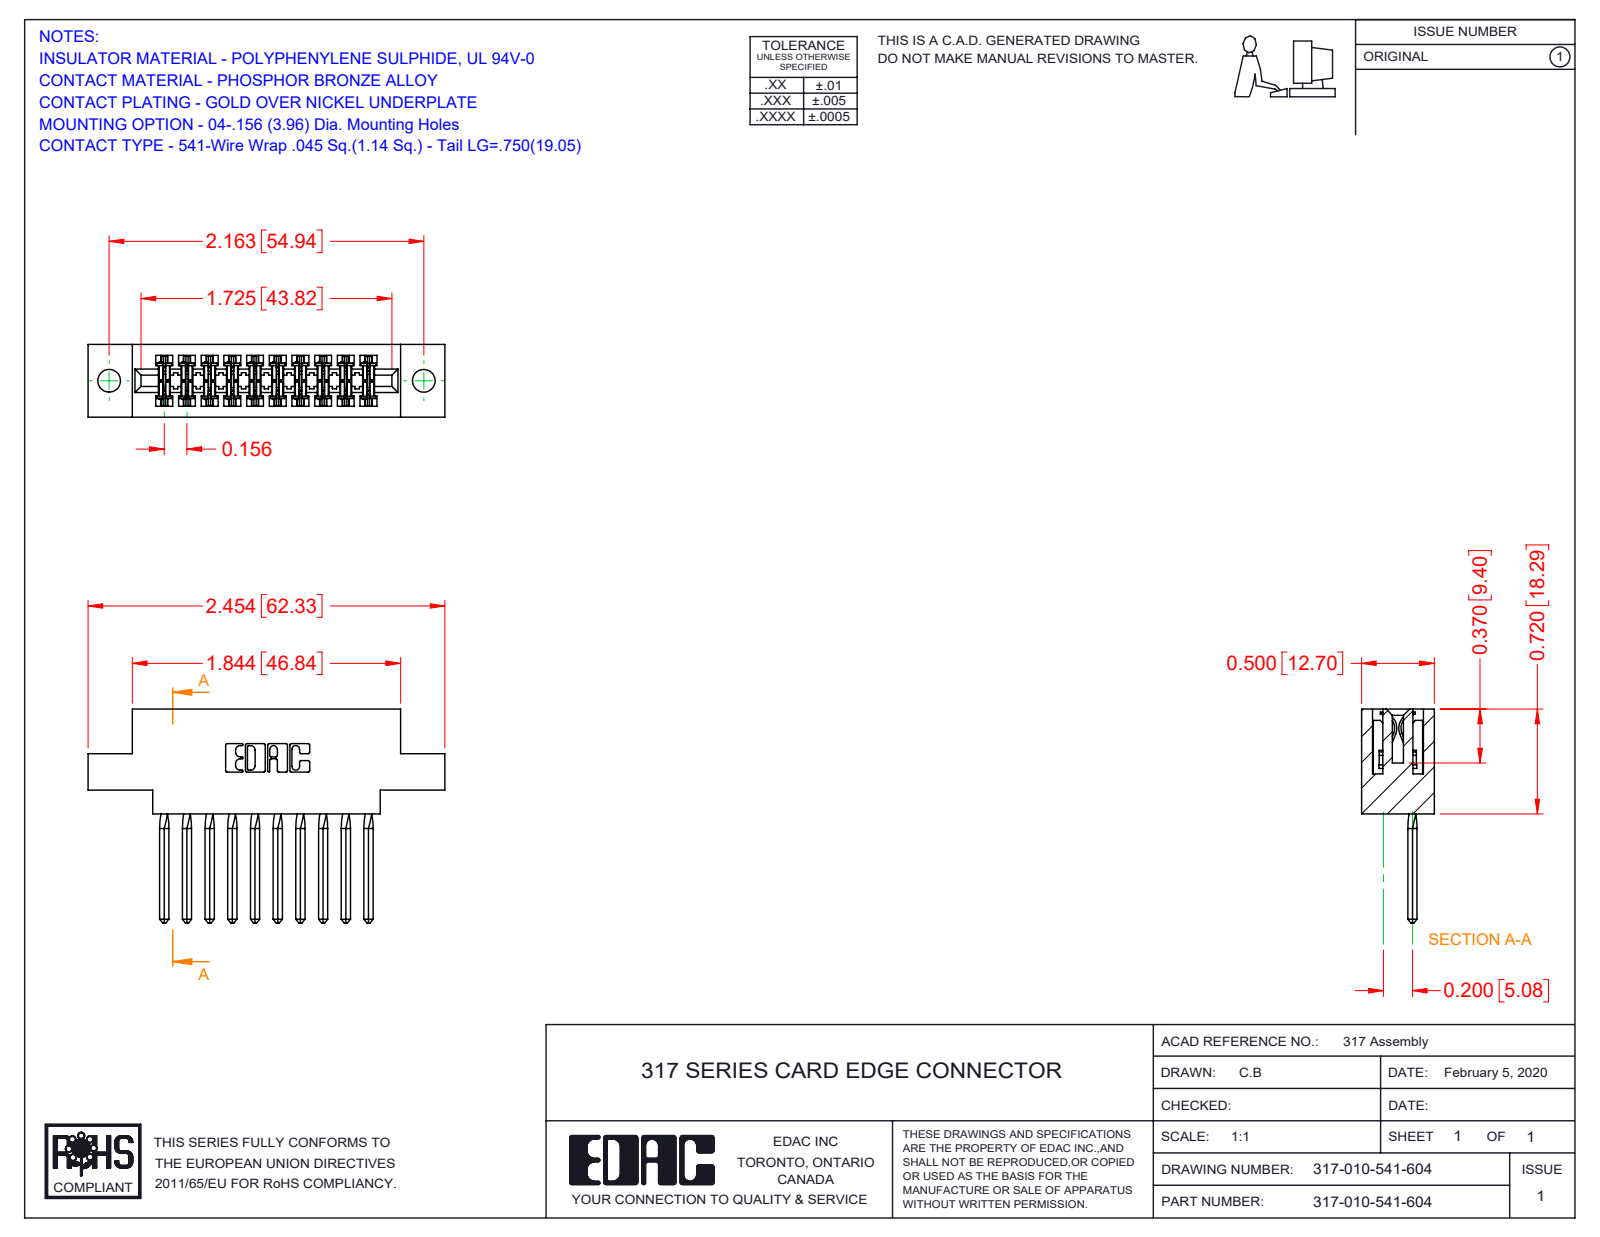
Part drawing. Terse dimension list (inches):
name: 317-010-541-604; 317 Part_.156 Dia - TH; 317-290-002_541
written by: SolidWorks 2016 (CONFIG_CONTROL_DESIGN)
unit: in
bodies: 11 solids, 1622 faces (1298 planar, 284 cylindrical, 40 other)
size: 2.454 × 1.47 × 0.5
volume: 0.551 in³; area: 17.86 in²
holes: 2× ⌀0.156
rounds: 22× R0.01, 20× R0.015, 6× R0.007, 6× R0.031, 3× R0.026, 2× R0.095, 2× R0.1, 2× R0.11
face distances: 0.5, 0.075, 0.425, 0.11, 0.065, 0.22, 0.331, 0.35, 0.156, 0.136
hole spacings: 2.163
